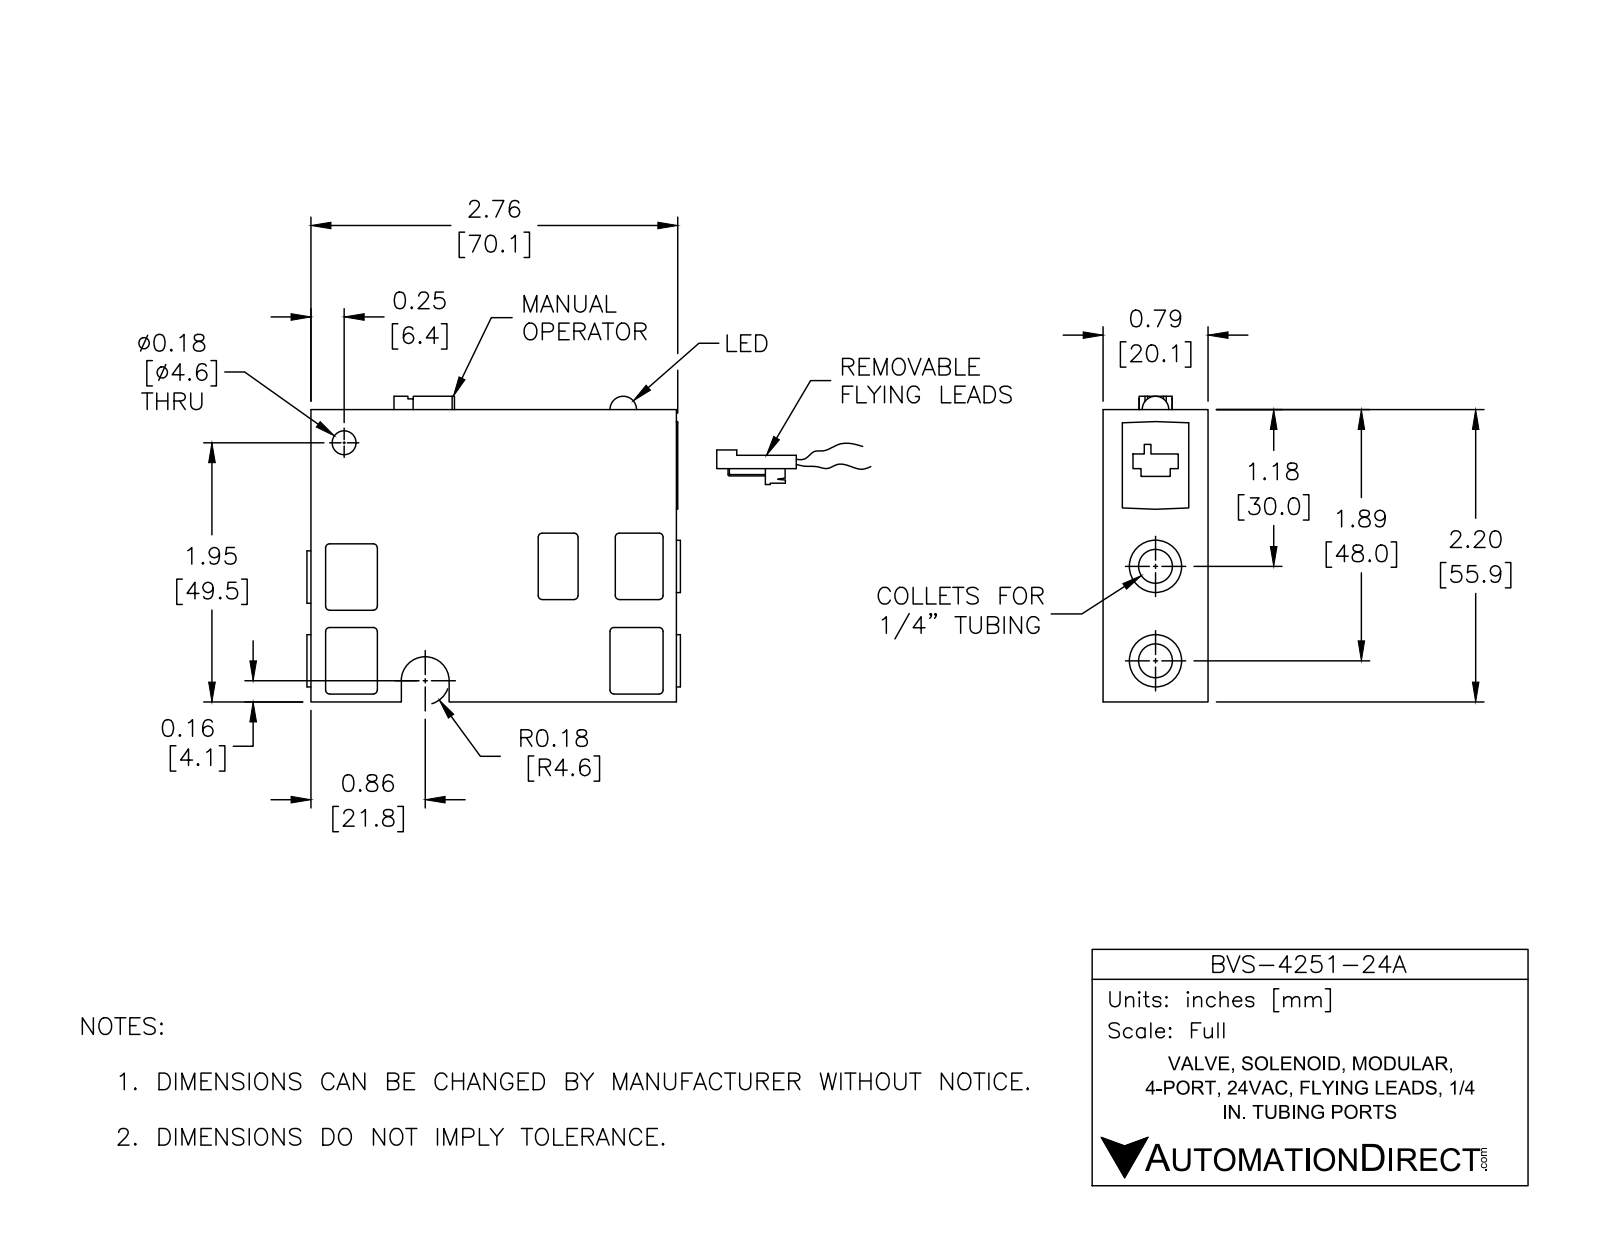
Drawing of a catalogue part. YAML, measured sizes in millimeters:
part_name: "BVS-4251-24A"
step_written_by: "SolidWorks 2016 (AUTOMOTIVE_DESIGN)"
units: millimeters
bodies: {solids: 1, faces: 173, planar: 85, cylindrical: 78, other: 10}
overall_size: [76.4, 58.4, 20.1]
volume: 71640
surface_area: 16180
round_holes:
  - {diameter: 6.5, count: 3}
  - {diameter: 2.5, count: 1}
  - {diameter: 4.6, count: 1}
round_bosses_or_shafts:
  - {diameter: 1.5, count: 6}
  - {diameter: 10, count: 3}
partial_cylinders:
  - {radius: 0.8, count: 20}
  - {radius: 0.5, count: 2}
  - {radius: 3.2, count: 1}
  - {radius: 4.6, count: 1}
face_to_face_distances: [20.1, 2.5, 55.9, 17.5, 69.9, 15, 12.7, 2.8, 67.3, 70.1]
hole_center_spacings: [2, 14, 16, 16, 18, 32]
